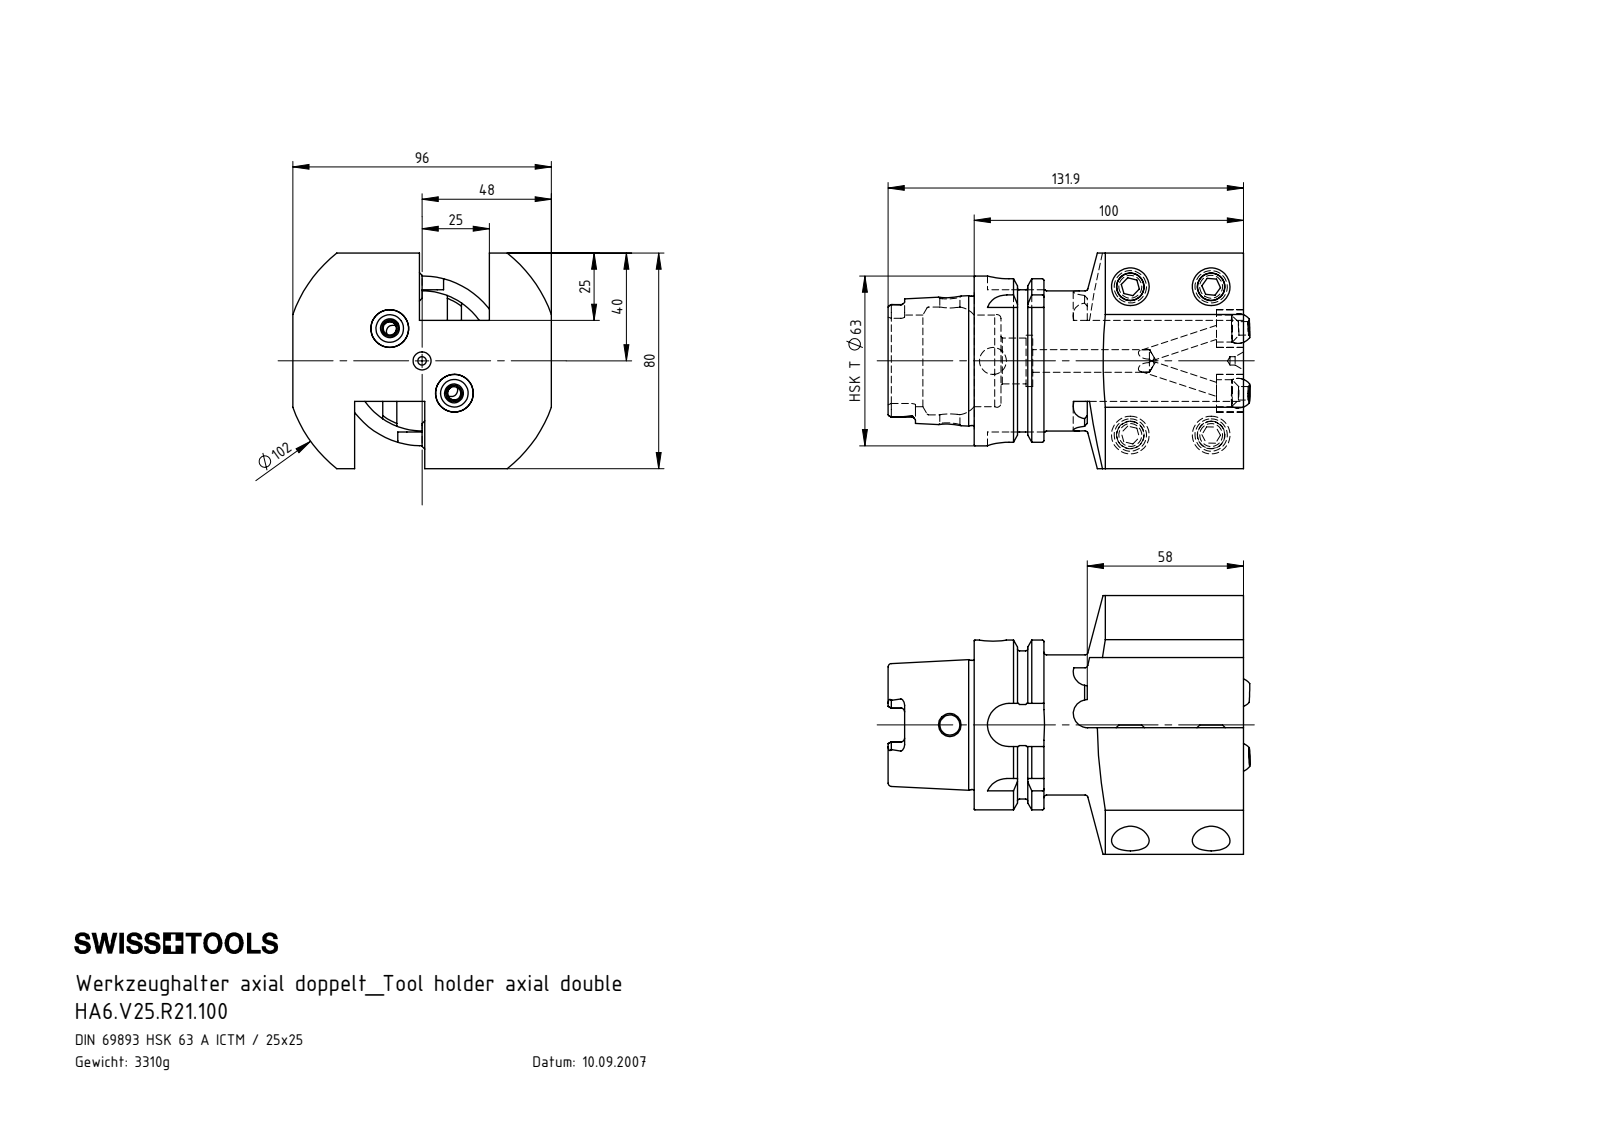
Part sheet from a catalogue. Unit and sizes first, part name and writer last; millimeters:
Units: millimetres
Overall size (bounding box): 134.71 × 96 × 80
Round holes (diameter × count): ⌀14 ×6, ⌀5 ×4, ⌀10.25 ×4, ⌀10 ×3, ⌀3.15 ×1, ⌀7.5 ×1, ⌀8.4 ×1, ⌀17 ×1, ⌀19 ×1, ⌀34 ×1, ⌀40 ×1
Round bosses / shafts (diameter × count): ⌀12 ×4, ⌀63 ×1, ⌀54.95 ×1, ⌀52 ×1, ⌀47.94 ×1
Partial cylindrical surfaces — rounded edges, fillets, slot ends (radius × count): R1.4 ×6, R2.88 ×4, R5.2 ×4, R8 ×4, R51 ×1
Main face-to-face distances: 25, 55, 23, 73, 26, 47, 49, 24, 80, 96
Hole centre spacings: 16.97, 30, 55, 57.94, 62.65, 85.54, 33.94
Volume: 422 672 mm³ · Surface area: 70 906 mm²
Bodies: 9 solids, 236 faces (105 planar, 62 cylindrical, 69 other)
Part name (STEP PRODUCT): ISO 4026 - M12 x 25; HA6-V25.R21.100_C; HA6.V25.R21.100; KU1-U14.001.012_2 (+2 more)
STEP written by: SolidWorks 2017 (AUTOMOTIVE_DESIGN)
